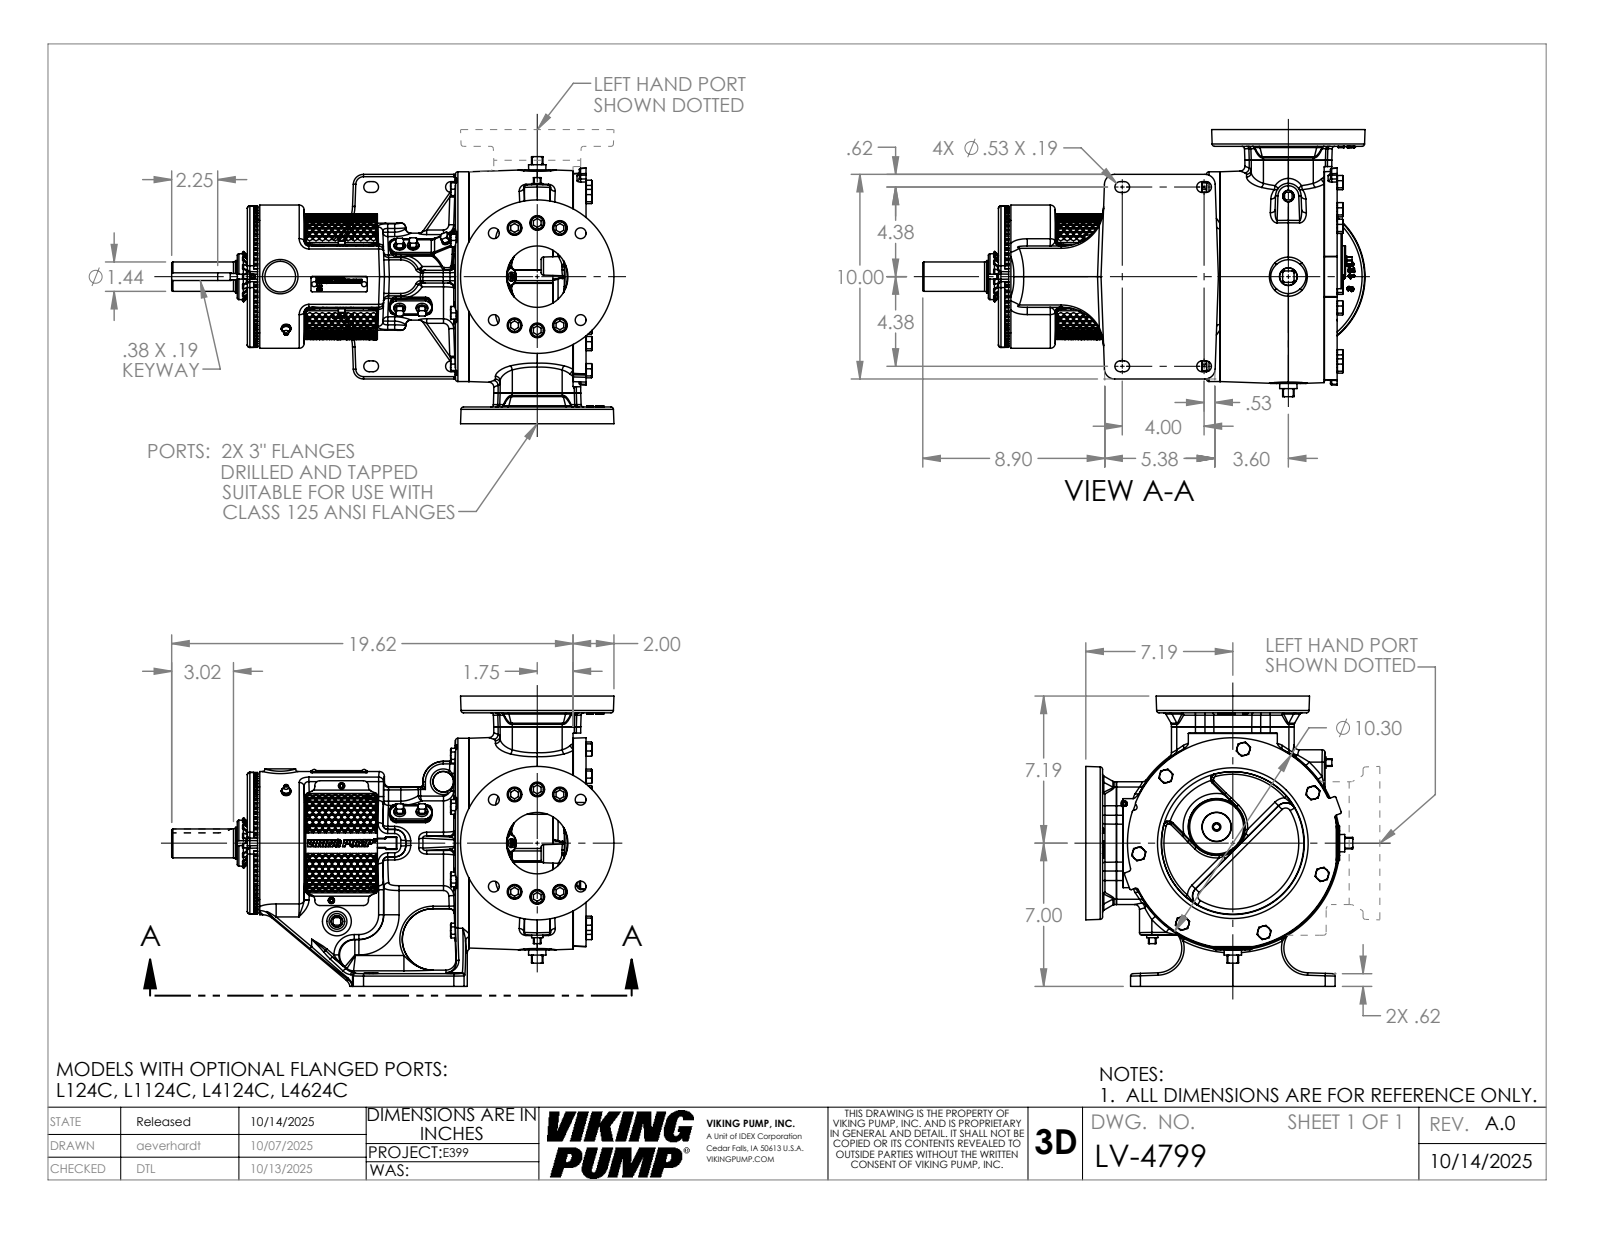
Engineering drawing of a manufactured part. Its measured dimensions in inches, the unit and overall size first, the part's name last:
Units: inches
Overall size (bounding box): 21.622 × 14.188 × 13.053
Round holes (diameter × count): ⌀0.469 ×12, ⌀0.719 ×12, ⌀0.25 ×9, ⌀0.531 ×8, ⌀1.094 ×8, ⌀0.199 ×6, ⌀0.159 ×3, ⌀0.266 ×2, ⌀0.313 ×2, ⌀3 ×2, ⌀0.453 ×1, ⌀1.577 ×1
Round bosses / shafts (diameter × count): ⌀0.66 ×12, ⌀0.437 ×12, ⌀0.625 ×10, ⌀0.625 ×5, ⌀0.312 ×3, ⌀0.19 ×3, ⌀10.25 ×1, ⌀7 ×1
Partial cylindrical surfaces — rounded edges, fillets, slot ends (radius × count): R0.063 ×109, R0.12 ×82, R0.069 ×74, R0.24 ×48, R0.01 ×30, R0.009 ×26, R0.03 ×18, R1 ×16
Main face-to-face distances: 14.187, 0.82, 13.367, 13.807, 3.537, 10.27, 0.5, 2.25, 1.382, 0.562
Hole centre spacings: 3, 4.243, 2.625, 1.375, 1.044, 1.136, 2.18, 2.18
Volume: 894 in³ · Surface area: 1 377 in²
Bodies: 1 solid, 5016 faces (1523 planar, 1035 cylindrical, 2458 other)
Part name (STEP PRODUCT): LV-4799
STEP written by: SolidWorks 2024 (AUTOMOTIVE_DESIGN)
